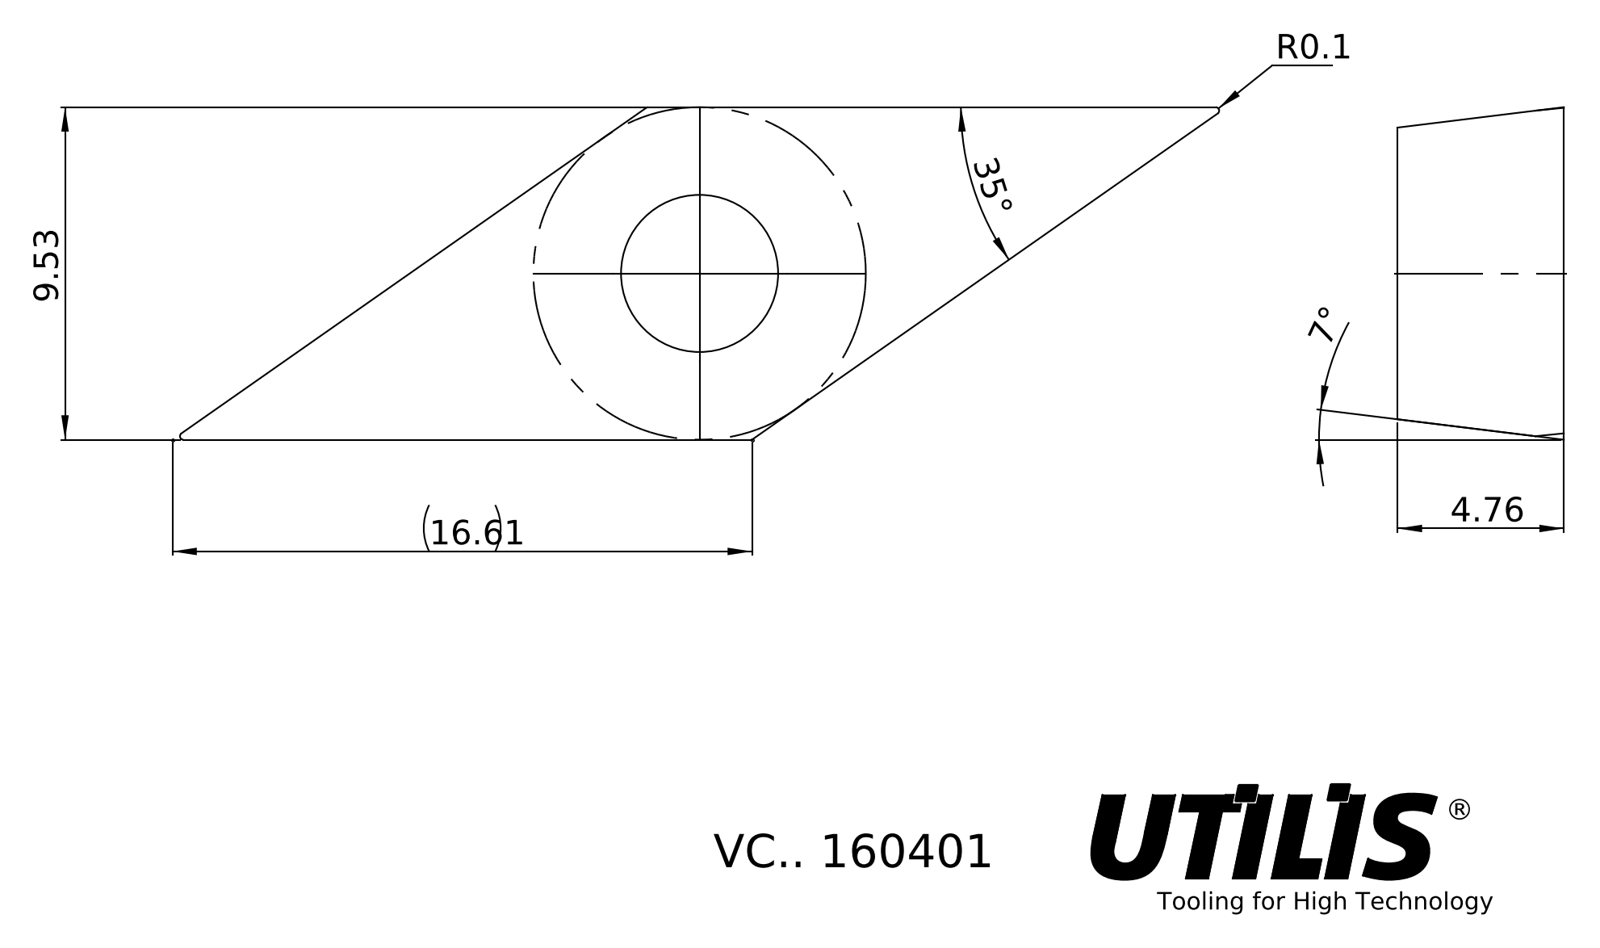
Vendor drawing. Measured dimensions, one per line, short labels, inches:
name: VC.. 160401
written by: SolidWorks 2016 (AUTOMOTIVE_DESIGN)
unit: in
bodies: 1 solid, 13 faces (2 planar, 2 cylindrical, 9 other)
size: 1.172 × 0.375 × 0.187
volume: 0.036 in³; area: 0.952 in²
holes: 1× ⌀0.177
face distances: 0.187
